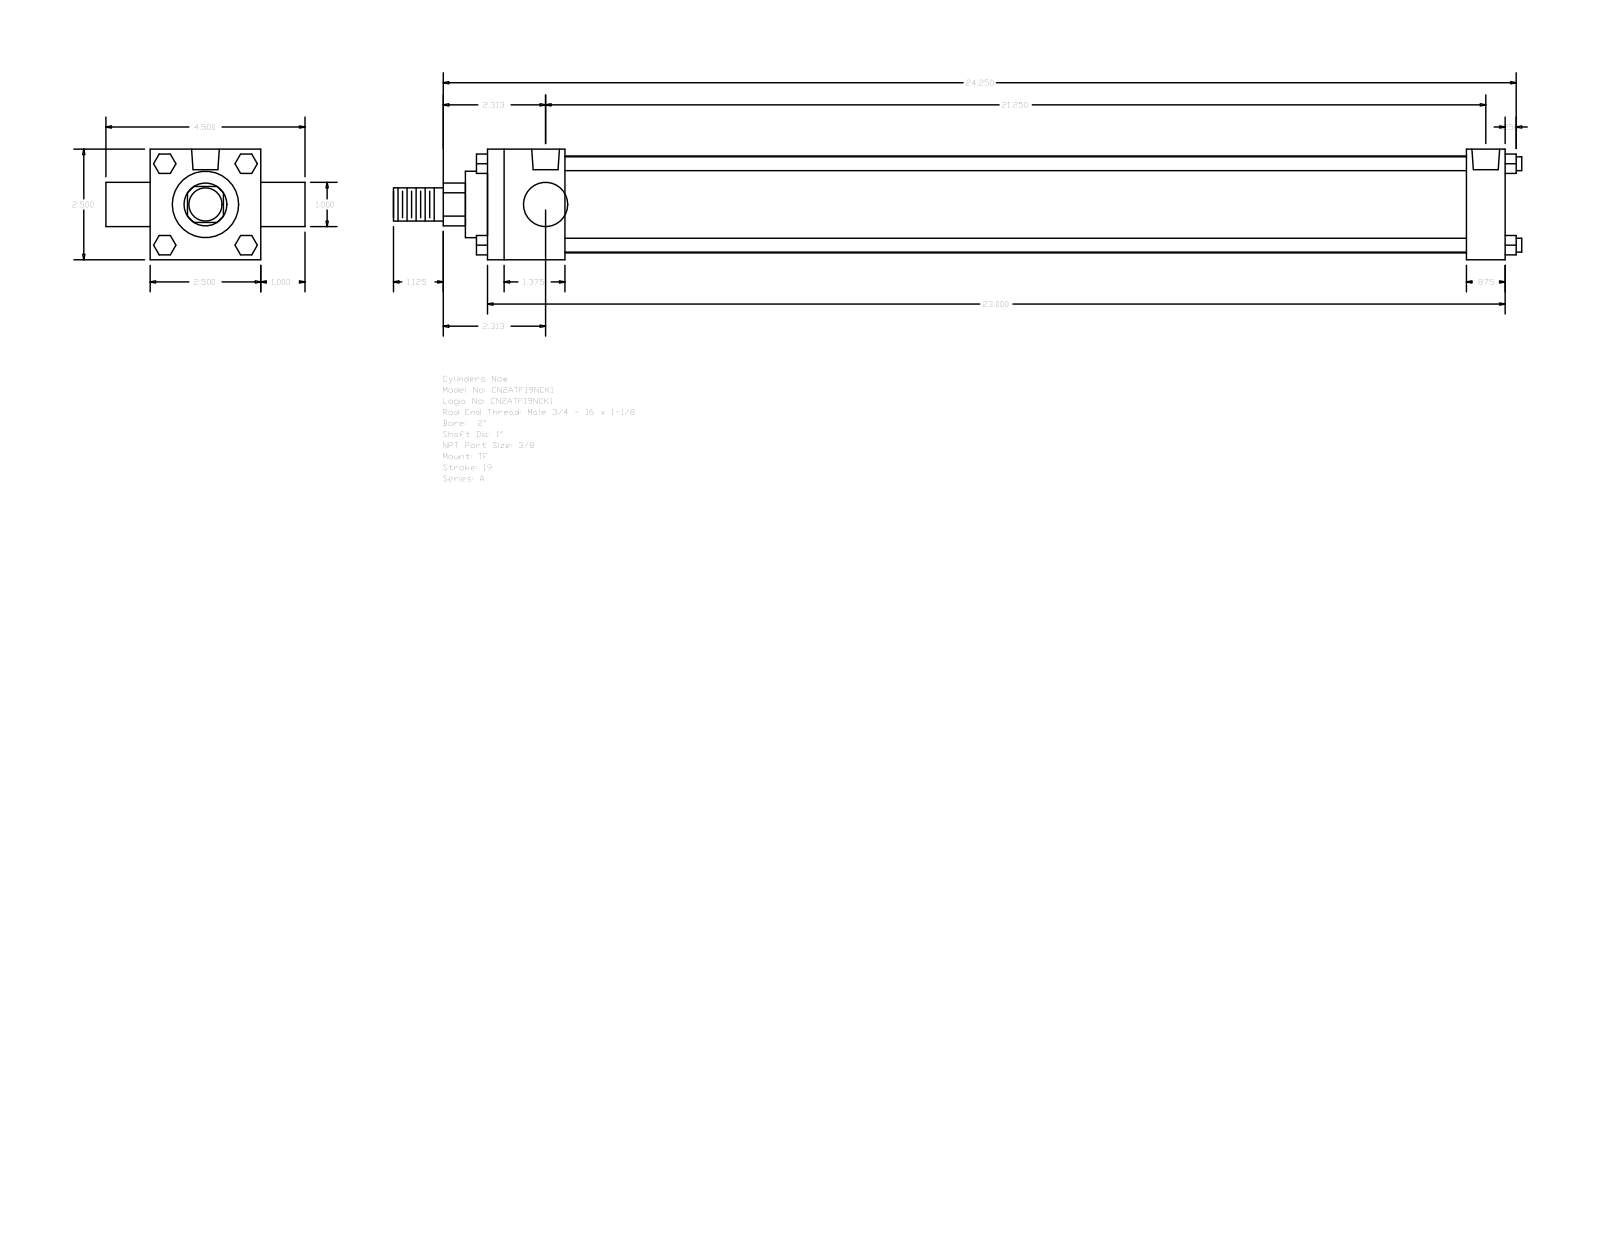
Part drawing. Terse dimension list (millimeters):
name: A_TF__0200_1
written by: GSSL Pune (CONFIG_CONTROL_DESIGN)
unit: mm
bodies: 0 solids, 120 faces (92 planar, 28 cylindrical, 0 other)
size: 647.7 × 114.3 × 63.5
holes: 3× ⌀5.56, 2× ⌀15.93
bosses: 4× ⌀7.94, 2× ⌀25.4, 1× ⌀55.63, 1× ⌀38.1, 1× ⌀19.05
rounds: 1× R12.29
face distances: 63.5, 584.2, 44.45, 561.98, 517.53, 539.75, 22.22, 25.4, 88.9, 596.9
hole spacings: 1.59, 3.98, 534.18, 535.77, 538.16, 539.75
